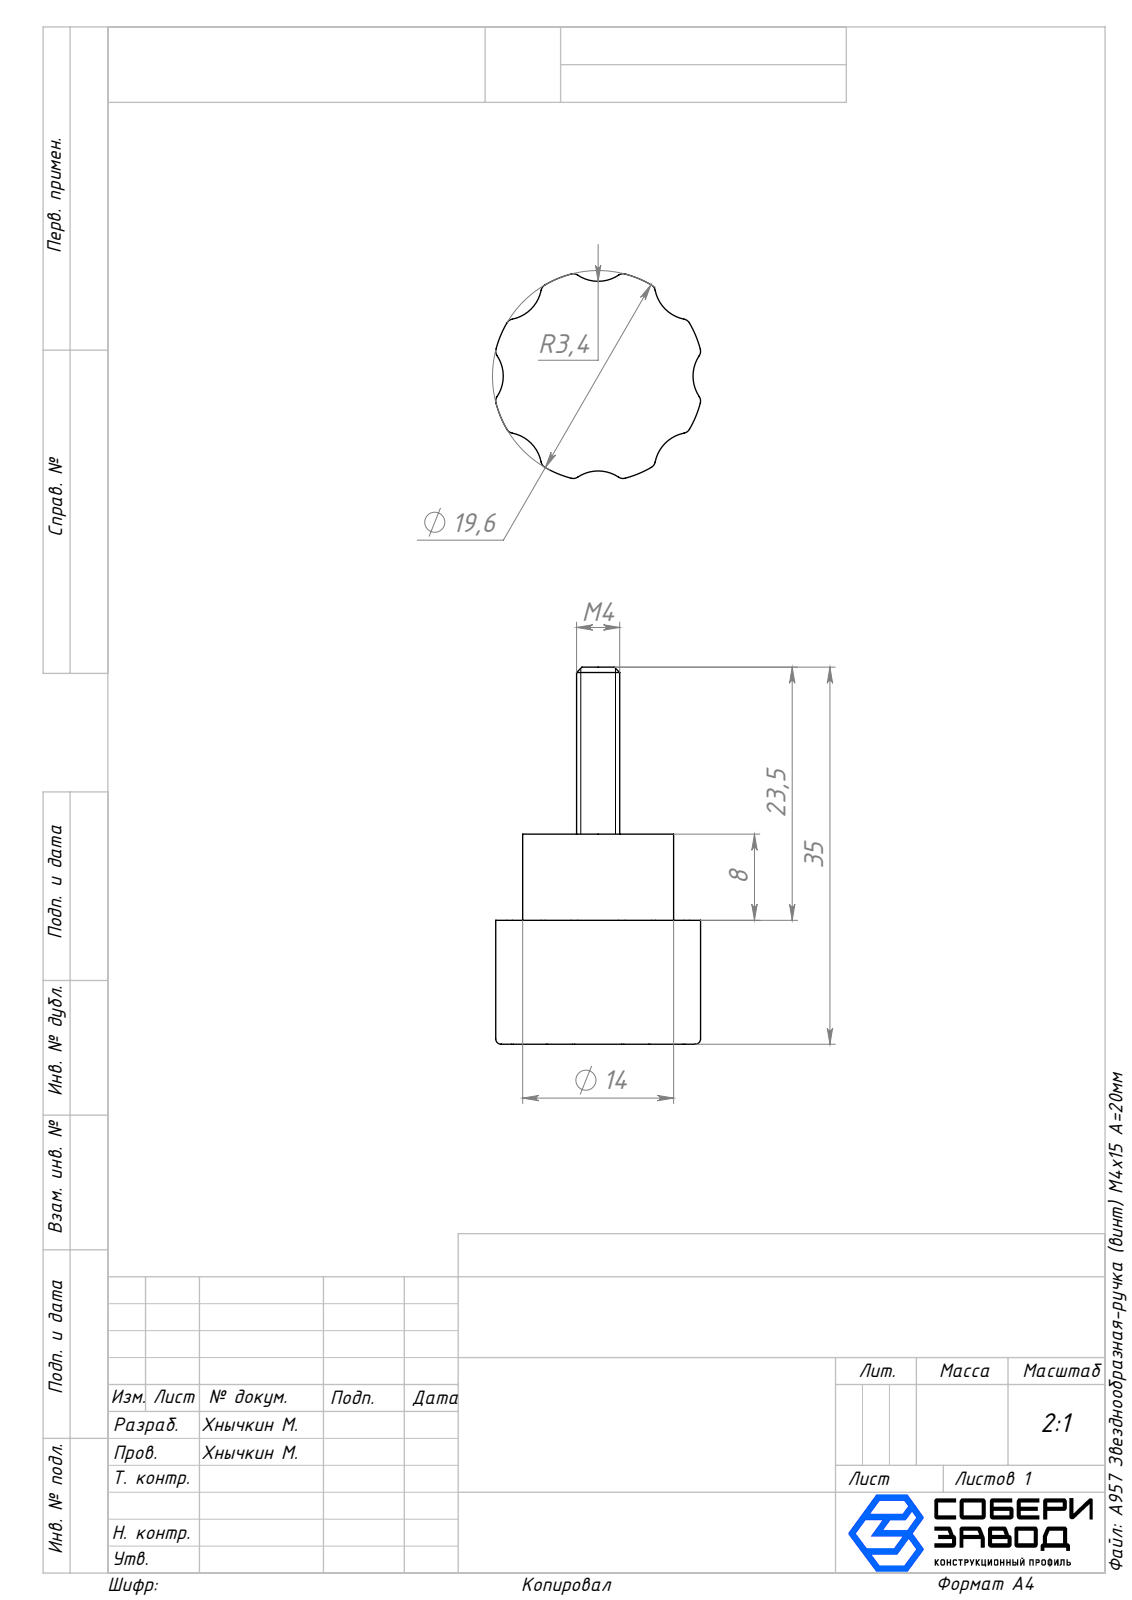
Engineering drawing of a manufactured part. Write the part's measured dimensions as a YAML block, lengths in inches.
part_name: "A957 Звезднообразная-ручка (винт) М4х15 А=20мм"
step_written_by: "SolidWorks 2025 (AUTOMOTIVE_DESIGN)"
units: inches
bodies: {solids: 1, faces: 85, planar: 5, cylindrical: 41, other: 39}
overall_size: [1.378, 0.748, 0.748]
volume: 0.269
surface_area: 3.24
round_holes:
  - {diameter: 0.276, count: 1}
round_bosses_or_shafts:
  - {diameter: 0.551, count: 1}
  - {diameter: 0.157, count: 1}
partial_cylinders:
  - {radius: 0.03, count: 16}
  - {radius: 0.135, count: 8}
  - {radius: 0.386, count: 1}
face_to_face_distances: [0.453, 0.768, 0.315, 1.378, 0.925, 0.61]
